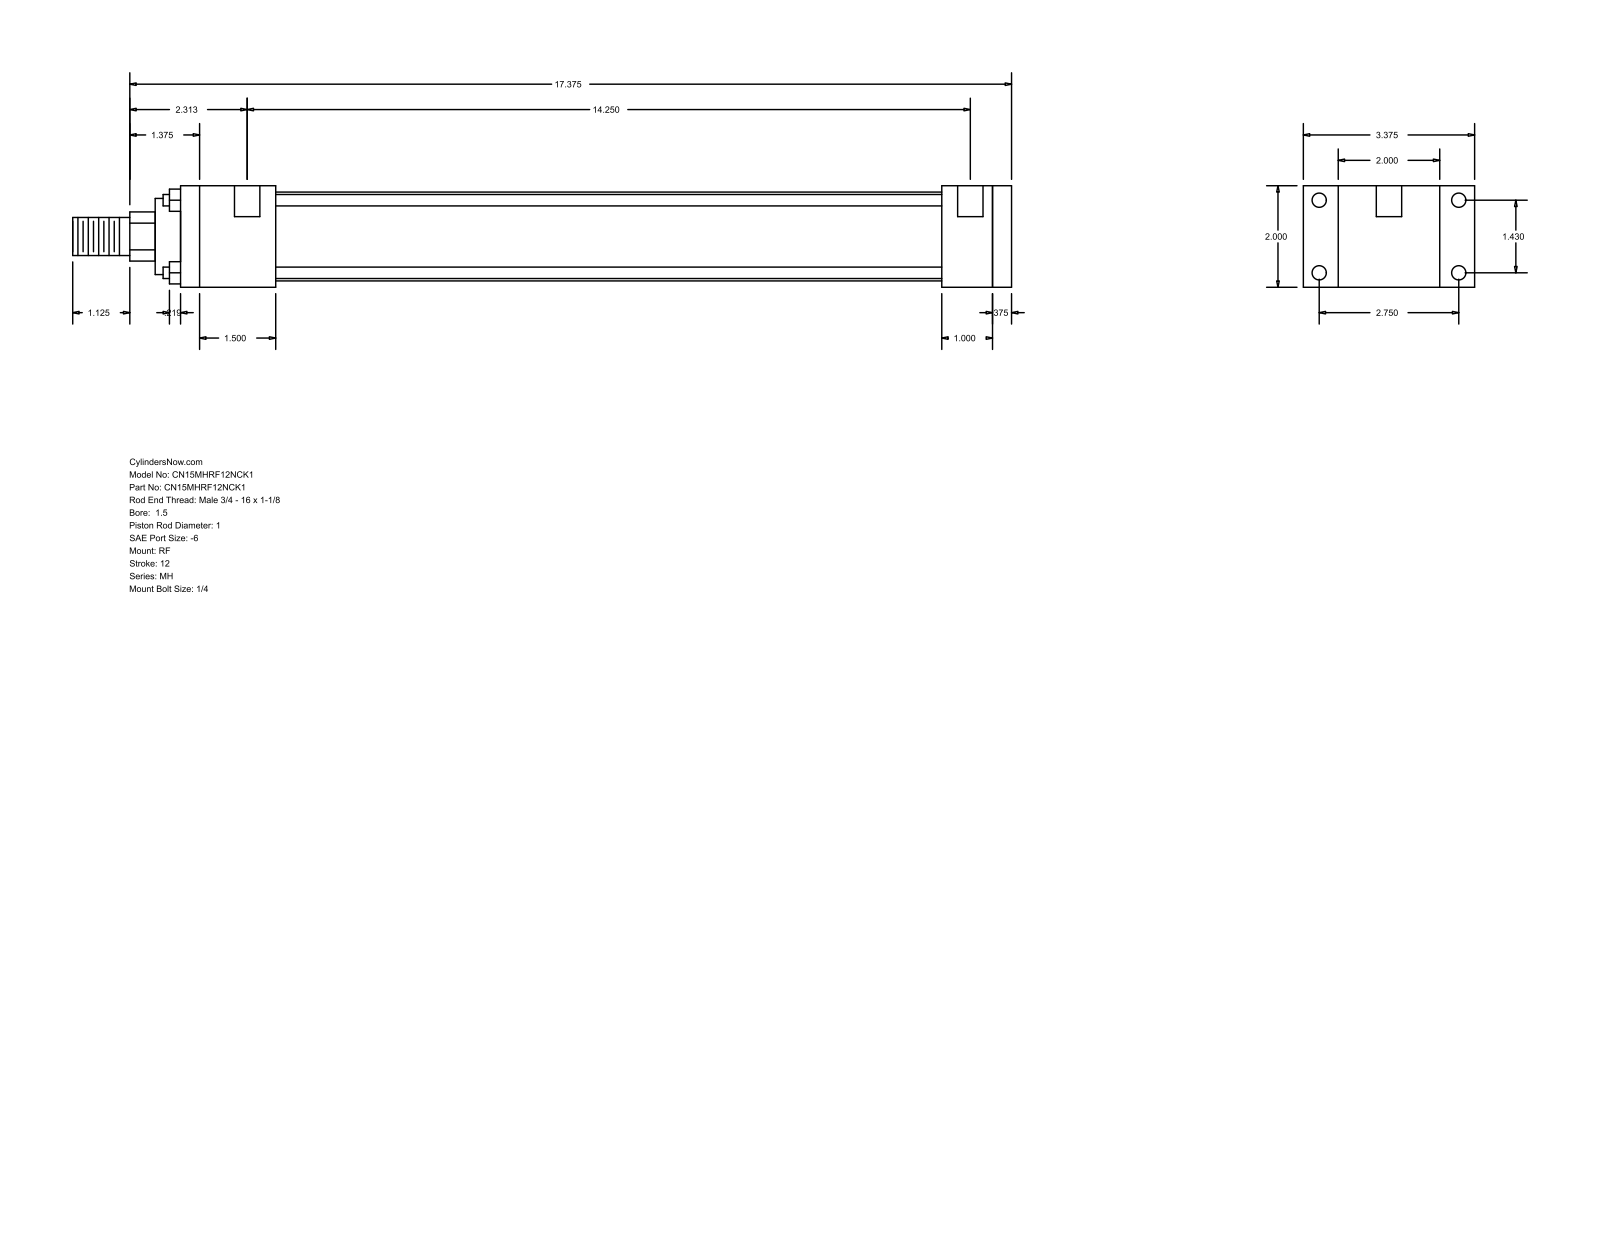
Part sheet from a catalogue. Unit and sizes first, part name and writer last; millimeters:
Units: millimetres
Overall size (bounding box): 469.9 × 85.72 × 50.8
Round holes (diameter × count): ⌀5.56 ×4, ⌀7.14 ×4, ⌀12.7 ×2
Round bosses / shafts (diameter × count): ⌀5.71 ×4, ⌀44.45 ×1, ⌀38.1 ×1, ⌀25.4 ×1, ⌀19.05 ×1
Partial cylindrical surfaces — rounded edges, fillets, slot ends (radius × count): R12.29 ×1
Main face-to-face distances: 50.8, 9.52, 406.4, 25.4, 415.92, 17.46, 68.26, 381, 34.92, 47.63
Hole centre spacings: 36.32, 69.84, 78.72, 365.13, 3.18, 361.95
Bodies: 0 solids, 92 faces (64 planar, 28 cylindrical, 0 other)
Part name (STEP PRODUCT): MH_RF__0150_1
STEP written by: GSSL Pune (CONFIG_CONTROL_DESIGN)
